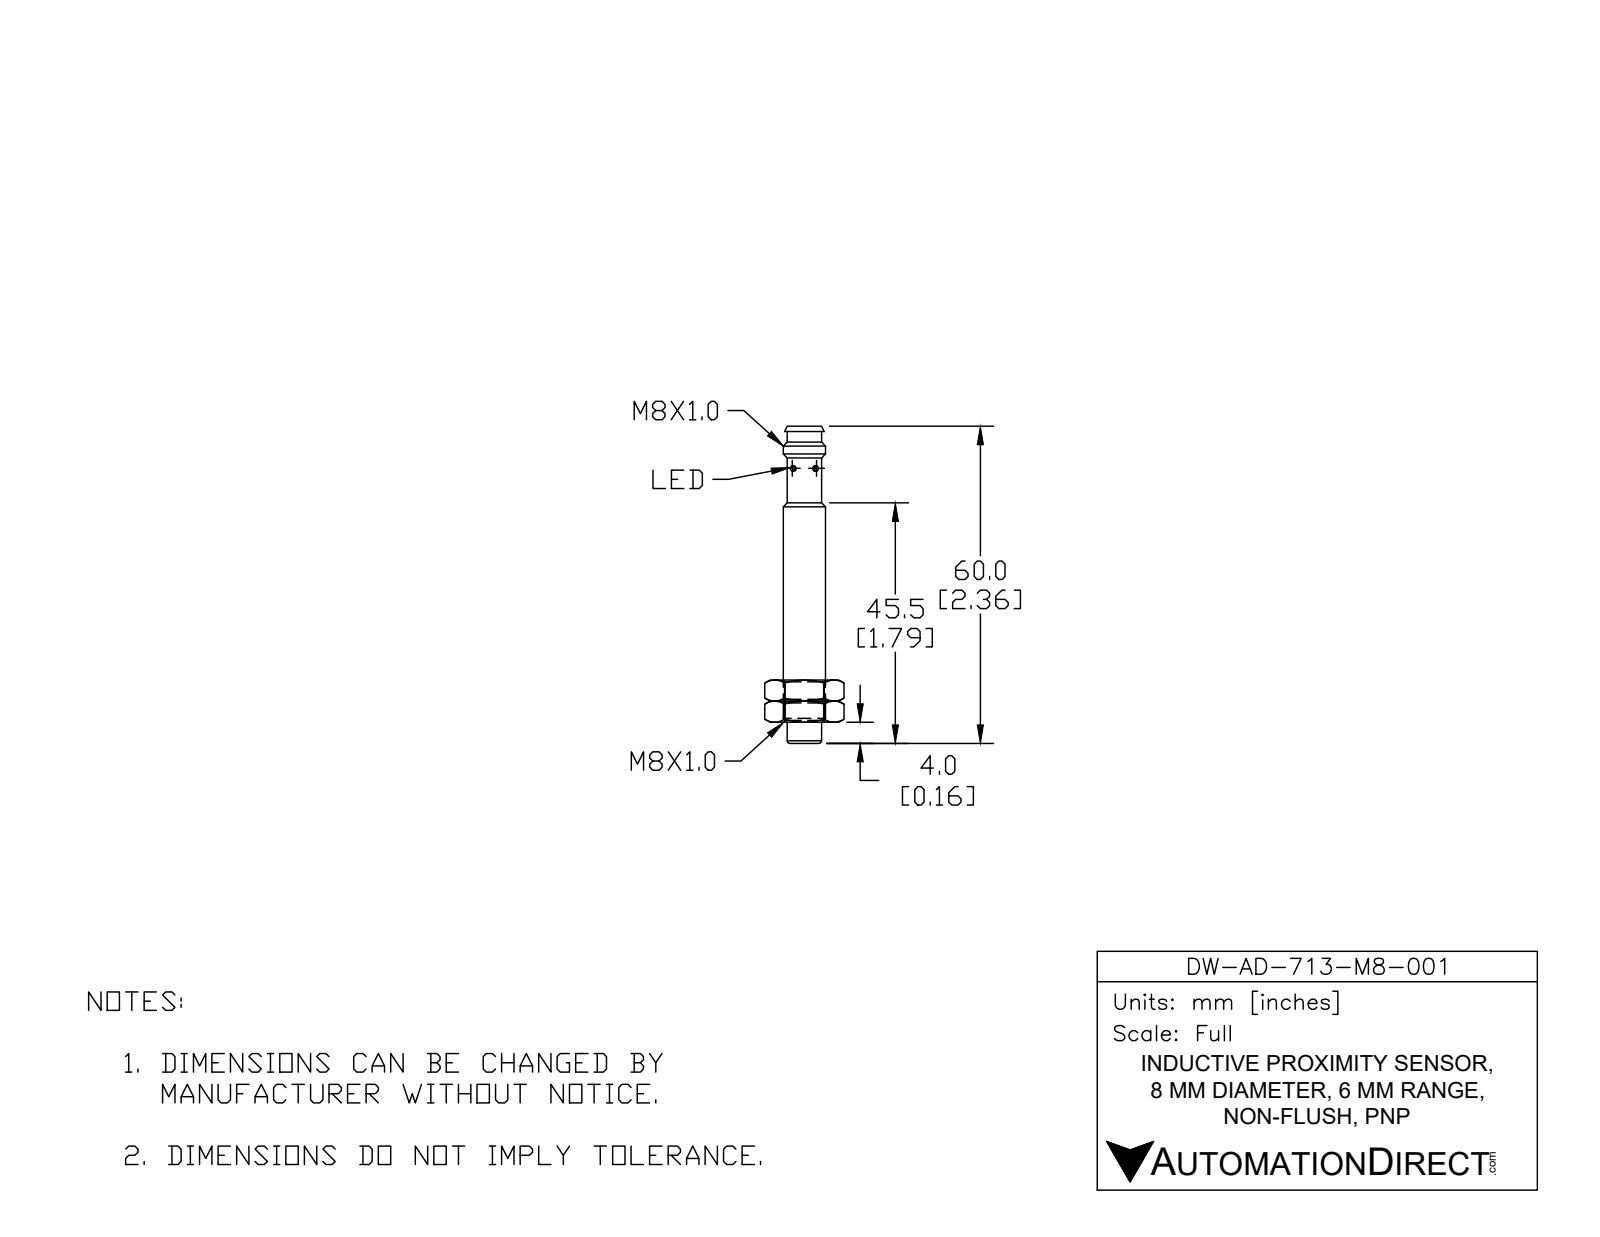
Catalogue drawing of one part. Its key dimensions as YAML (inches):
part_name: "DW-AS-713-M8-001"
step_written_by: "SolidWorks 2017 (AUTOMOTIVE_DESIGN)"
units: inches
bodies: {solids: 1, faces: 49, planar: 15, cylindrical: 22, other: 12}
overall_size: [2.362, 0.315, 0.315]
volume: 0.16
surface_area: 2.613
round_holes:
  - {diameter: 0.071, count: 2}
round_bosses_or_shafts:
  - {diameter: 0.039, count: 3}
  - {diameter: 0.315, count: 1}
  - {diameter: 0.272, count: 1}
  - {diameter: 0.256, count: 1}
  - {diameter: 0.236, count: 1}
partial_cylinders:
  - {radius: 0.118, count: 1}
face_to_face_distances: [2.179, 0.157, 2.362, 0.183, 2.002, 0.177, 0.36]
